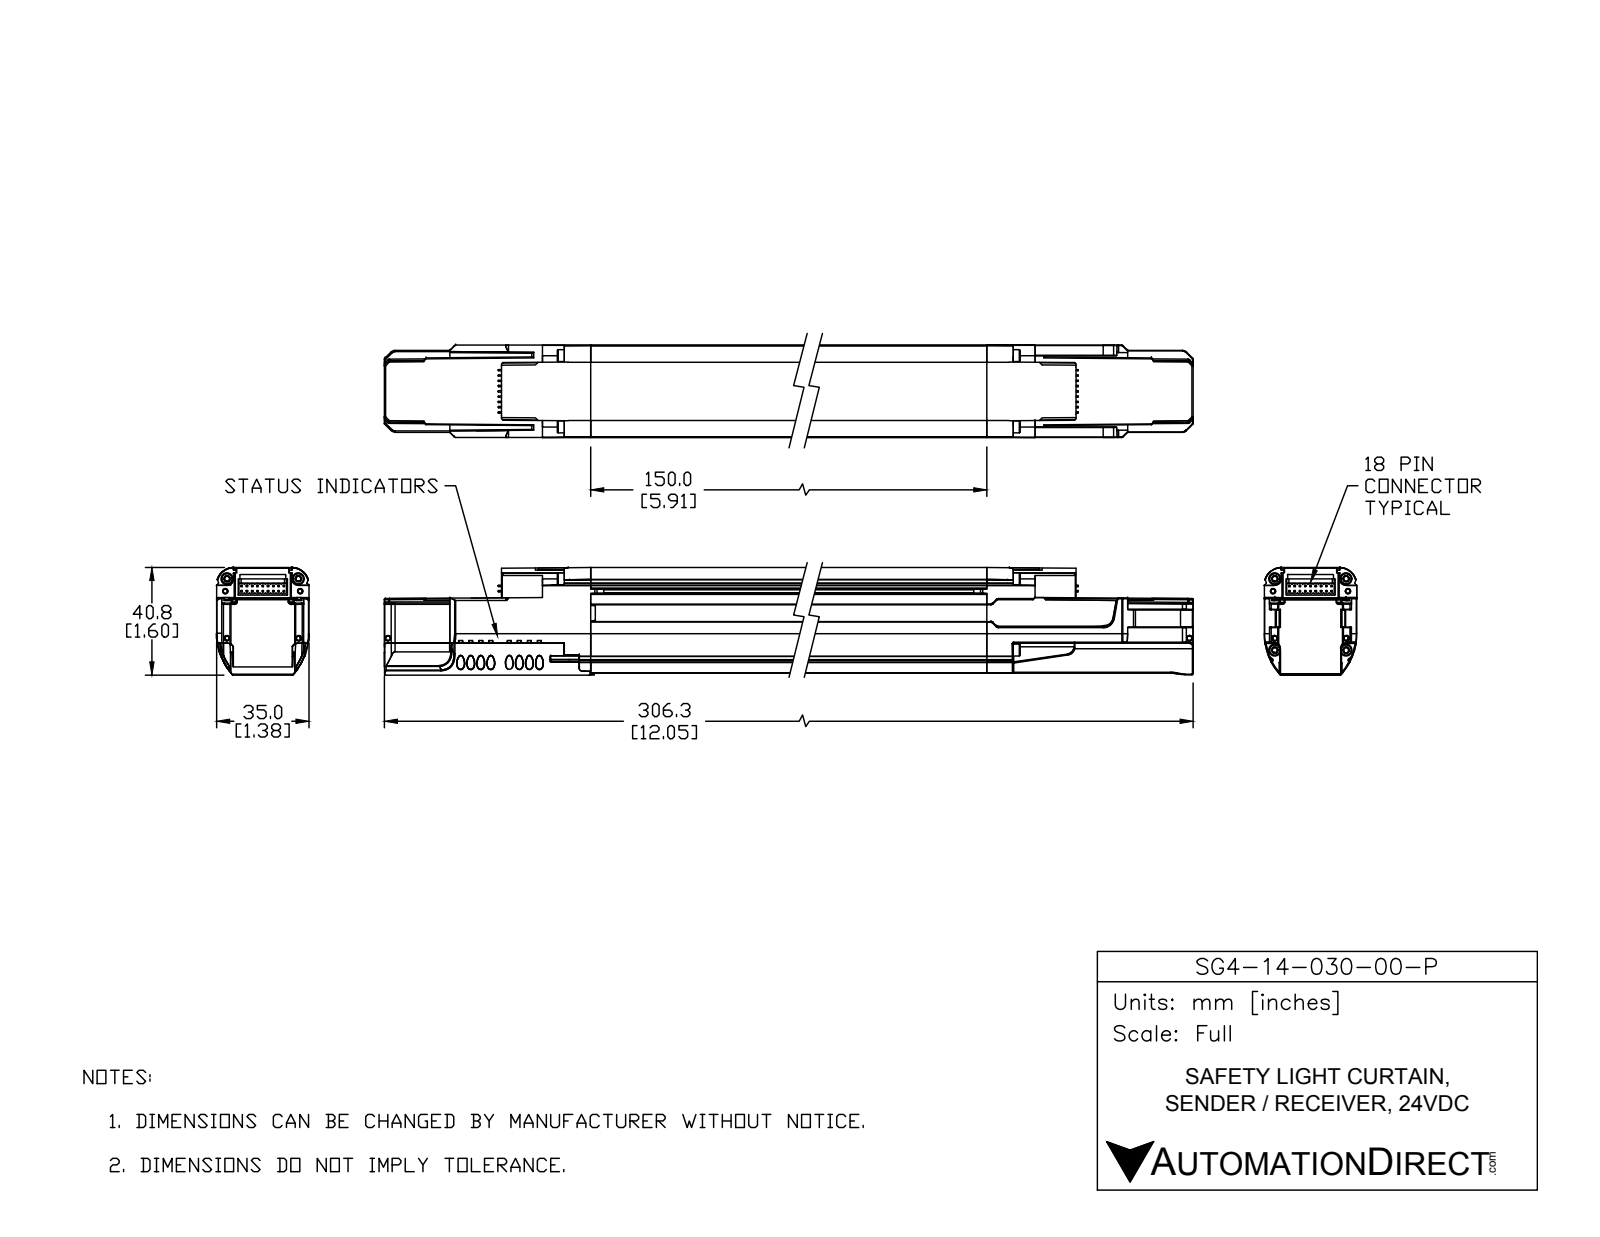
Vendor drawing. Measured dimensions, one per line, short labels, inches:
name: SG4-14-030-OO-P
written by: SolidWorks 2017 (AUTOMOTIVE_DESIGN)
unit: in
bodies: 16 solids, 534 faces (362 planar, 110 cylindrical, 62 other)
size: 12.063 × 2.58 × 2.023
volume: 21.51 in³; area: 138.7 in²
holes: 6× ⌀0.07, 4× ⌀0.1, 4× ⌀0.165, 4× ⌀0.209, 4× ⌀0.26, 1× ⌀0.065, 1× ⌀0.065
bosses: 4× ⌀0.394, 4× ⌀0.197
rounds: 16× R0.106, 8× R0.118, 4× R0.1, 4× R0.11, 2× R0.08, 2× R0.12, 2× R0.123, 2× R0.125
face distances: 0.06, 0.084, 0.024, 1.49, 1.466, 1.55, 0.118, 5.91, 1.057, 1.325
hole spacings: 0.569, 4.331, 0.02, 0.204, 0.207, 0.207, 0.227, 0.71
